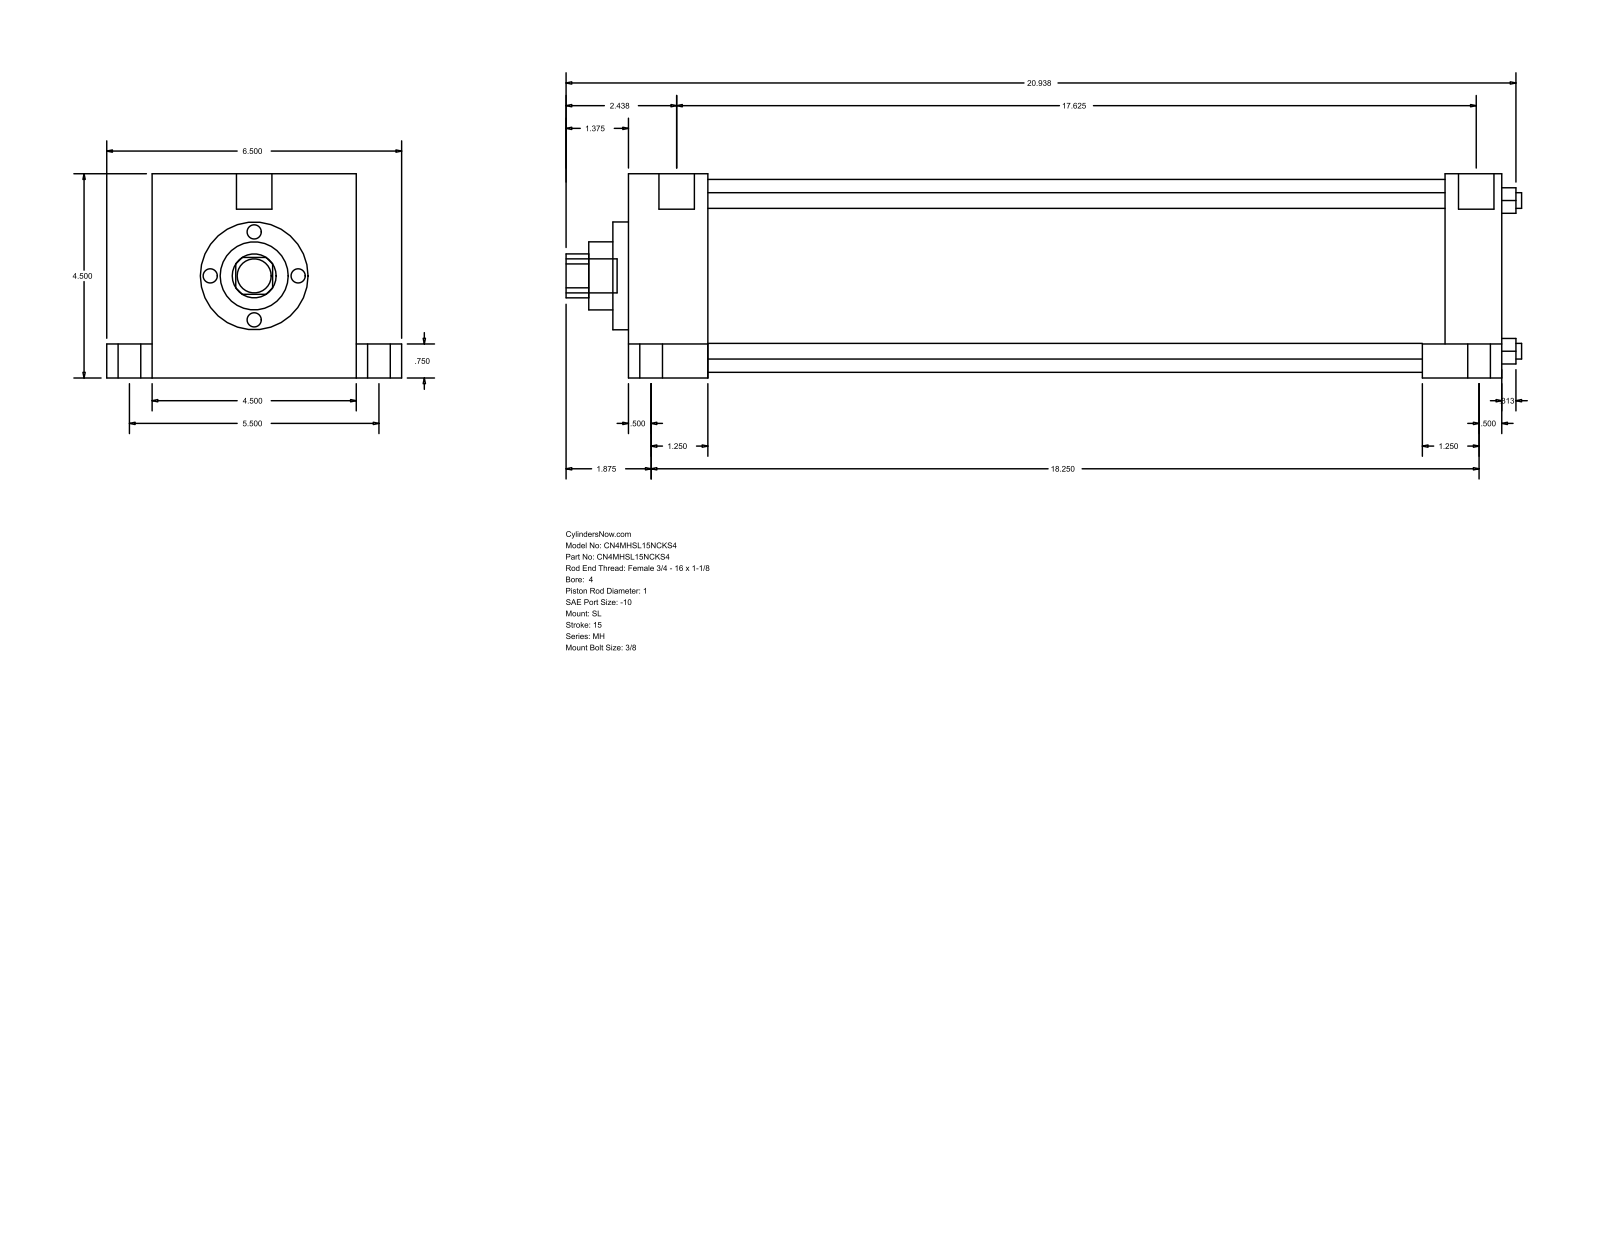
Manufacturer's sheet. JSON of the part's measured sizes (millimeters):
{"part_name": "MH_SL__0400_1", "step_written_by": "GSSL Pune (CONFIG_CONTROL_DESIGN)", "units": "millimeters", "bodies": {"solids": 0, "faces": 110, "planar": 77, "cylindrical": 33, "other": 0}, "overall_size": [534.99, 165.1, 114.3], "round_holes": [[8.76, 4], [25.4, 1], [38.1, 1], [60.33, 1], [107.95, 1]], "round_bosses_or_shafts": [[19.05, 5], [12.7, 4], [8.73, 4], [19.84, 2]], "partial_cylinders_radius": [[12.29, 1]], "face_to_face_distances": [114.3, 488.96, 44.46, 444.5, 457.2, 412.74, 31.76, 25.4, 139.7, 19.05], "hole_center_spacings": [59.62, 84.32, 119.25]}
